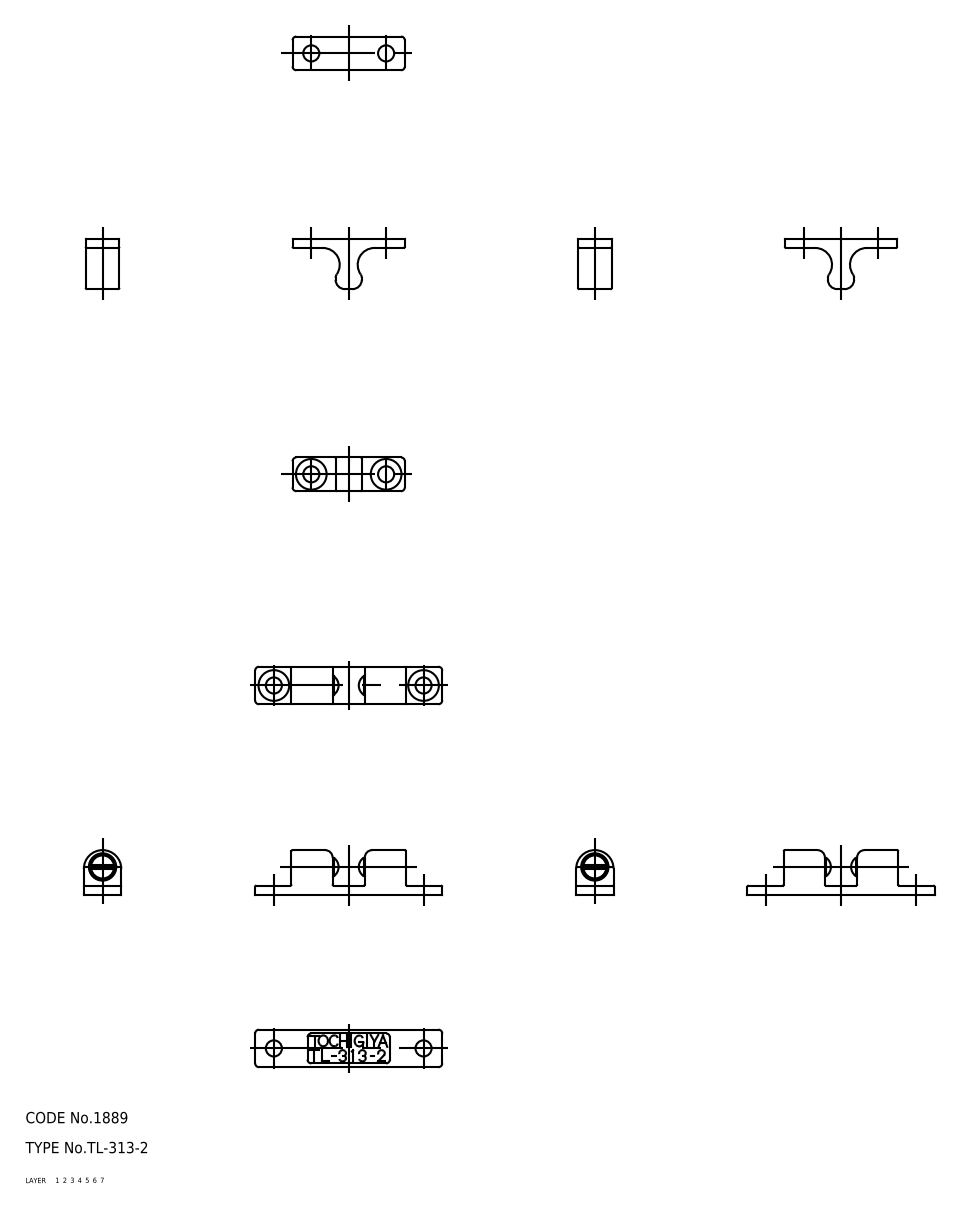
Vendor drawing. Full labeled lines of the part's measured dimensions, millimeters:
Part name (STEP PRODUCT): ball; screw; keeper; housing (+1 more)
STEP written by: CADfix (AUTOMOTIVE_DESIGN)
Units: millimetres
Bodies: 6 solids, 98 faces (0 planar, 0 cylindrical, 98 other)
Overall size (bounding box): 52.66 × 50 × 10
Volume: 3 860 mm³ · Surface area: 3 923 mm²
